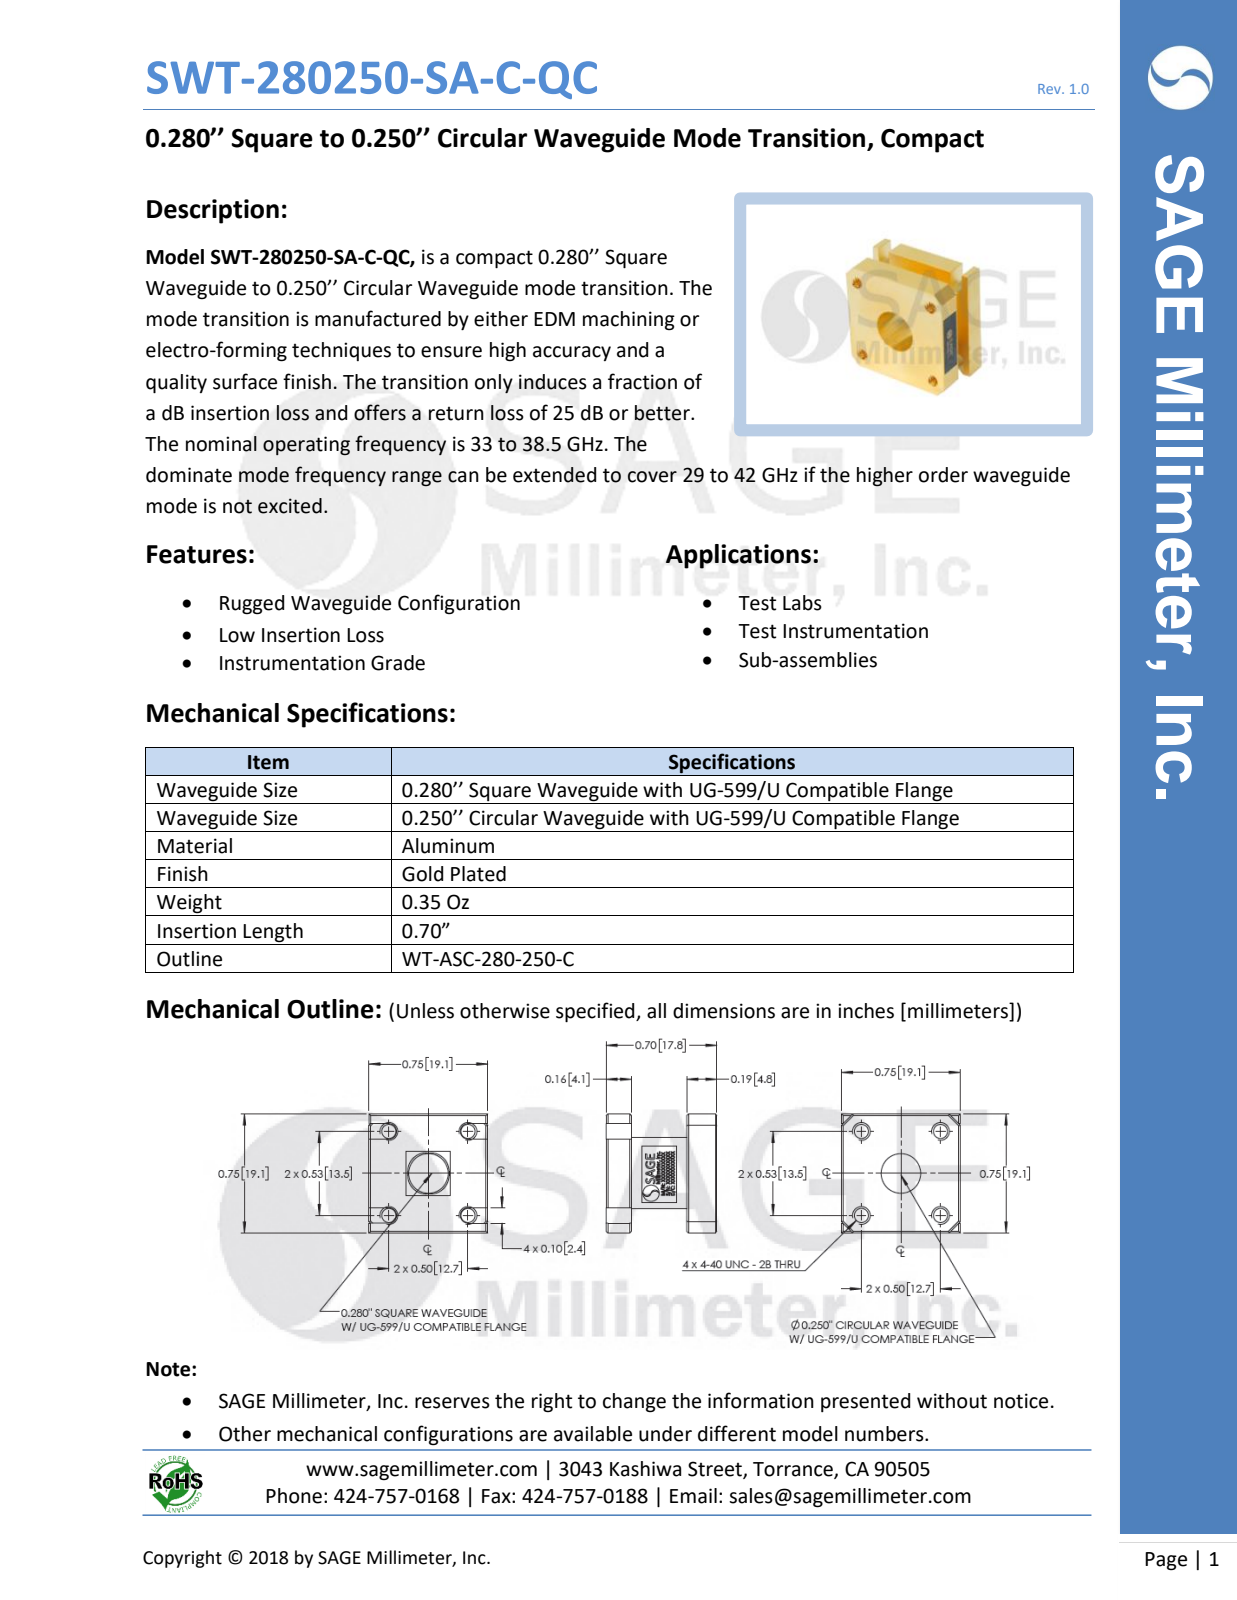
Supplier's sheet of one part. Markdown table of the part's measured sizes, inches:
| quantity | value |
| --- | --- |
| part name | SWT-280250-SA-C-QC |
| STEP written by | SolidWorks 2016 (CONFIG_CONTROL_DESIGN) |
| units | inches |
| bodies | 1 solid, 84 faces (66 planar, 18 cylindrical, 0 other) |
| overall size | 0.75 × 0.75 × 0.7 |
| volume | 0.235 in³ |
| surface area | 3.603 in² |
| round holes (diameter × count) | 0.089 × 4, 0.25 × 1 |
| round bosses / shafts (diameter × count) | 0.45 × 1 |
| partial cylindrical surfaces (radius × count) | 0.048 × 4 |
| main face-to-face distances | 0.7, 0.75, 0.19, 0.51, 0.54, 0.35, 0.16, 0.695, 0.096, 0.53 |
| hole center spacings | 0.364, 0.5, 0.53, 0.729 |
